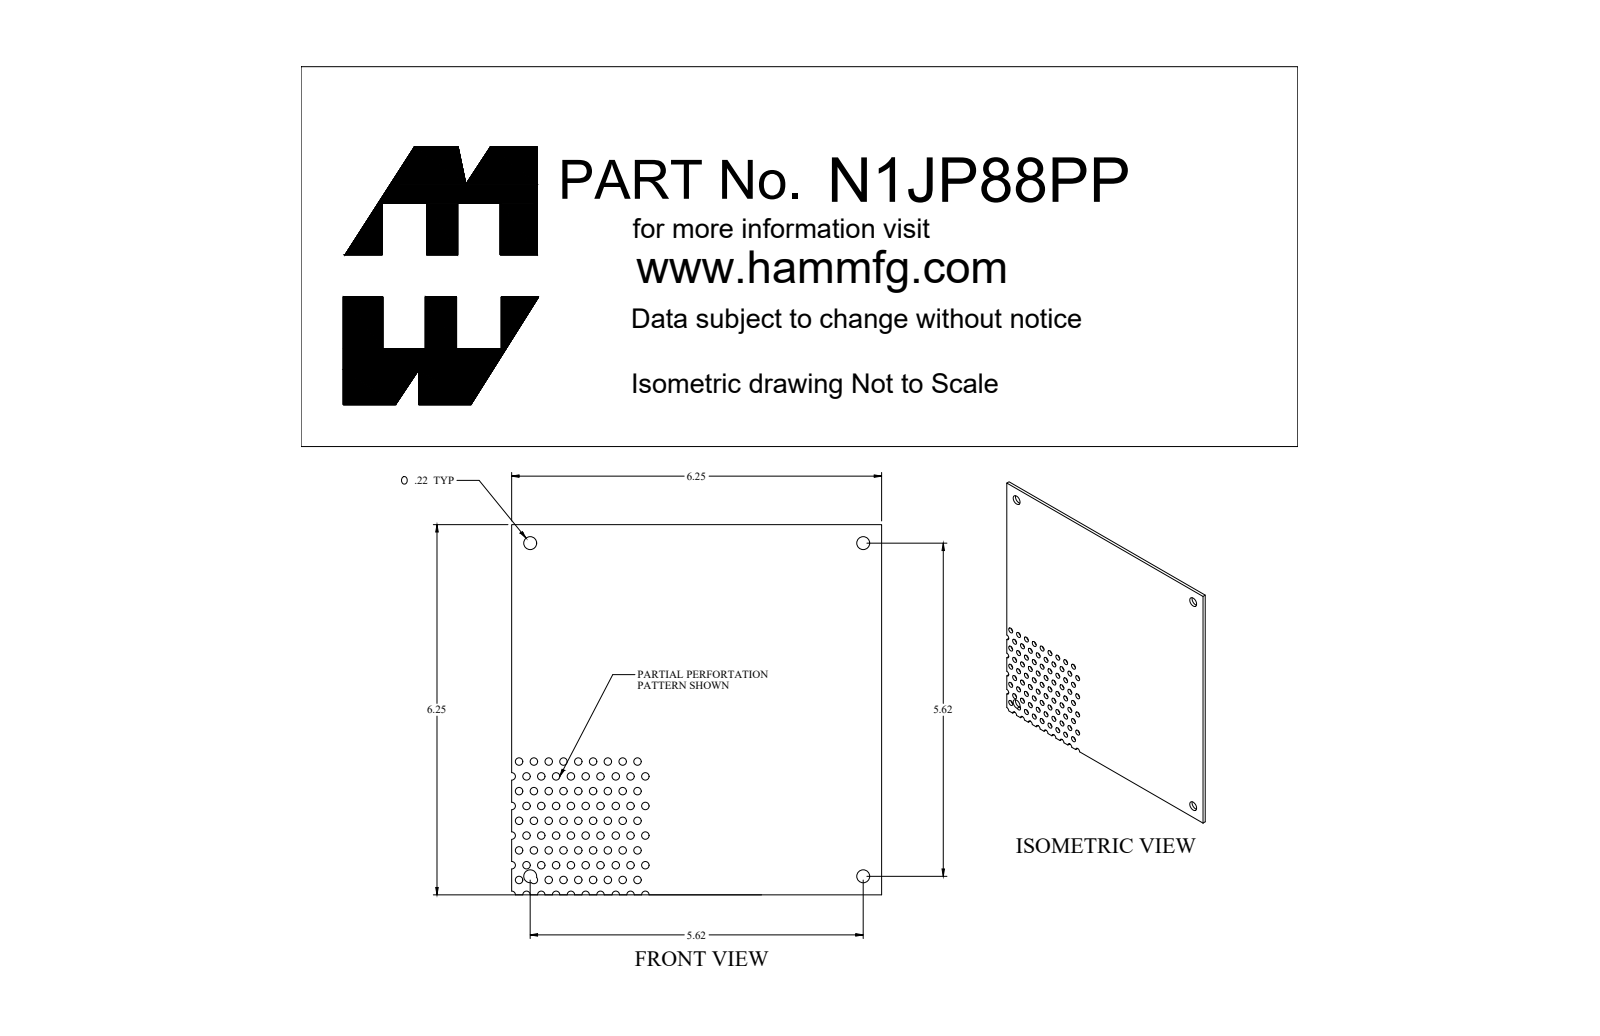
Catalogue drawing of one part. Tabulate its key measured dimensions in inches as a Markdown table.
| quantity | value |
| --- | --- |
| part name | N1JP88PP |
| STEP written by | SolidWorks 2018 (AUTOMOTIVE_DESIGN) |
| units | inches |
| bodies | 1 solid, 203 faces (19 planar, 184 cylindrical, 0 other) |
| overall size | 6.25 × 6.25 × 0.072 |
| volume | 2.725 in³ |
| surface area | 80.02 in² |
| round holes (diameter × count) | 0.125 × 58, 0.125 × 22, 0.218 × 4 |
| partial cylindrical surfaces (radius × count) | 0.063 × 8, 0.062 × 7 |
| main face-to-face distances | 0.072, 6.25 |
| hole center spacings | 0.25, 0.5, 0.559, 0.707, 0.75, 0.28, 0.451, 0.902 |
